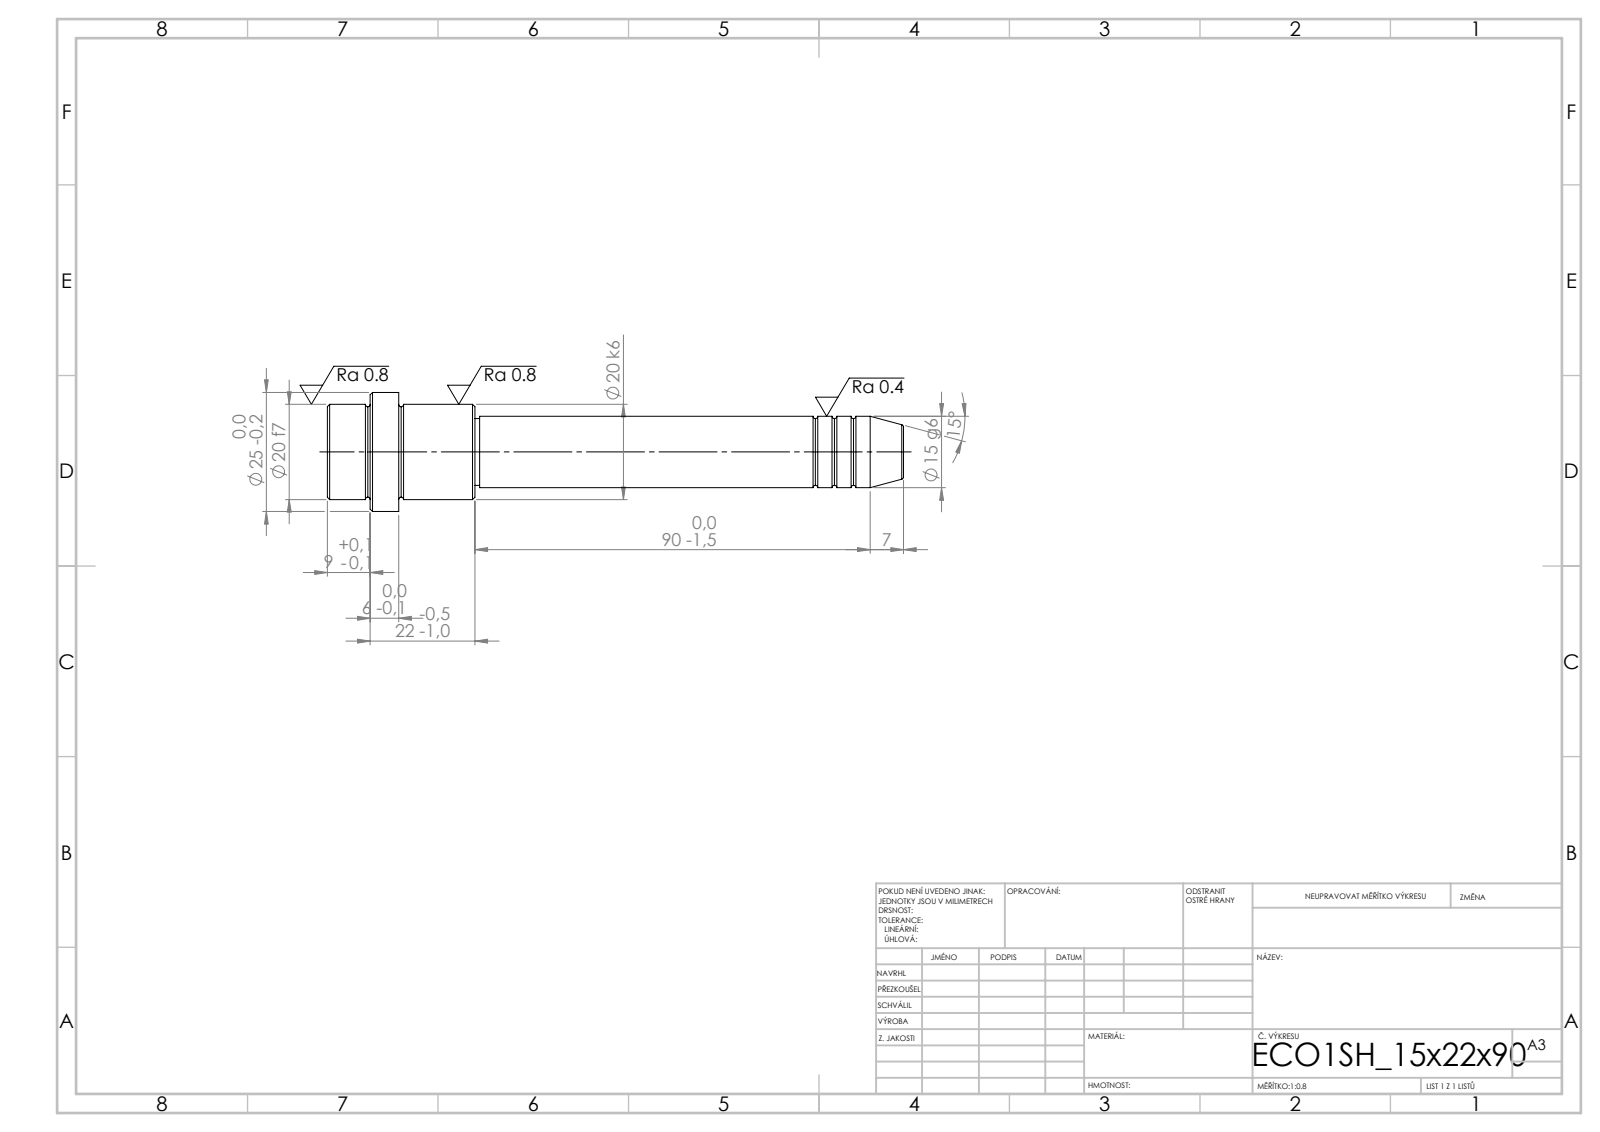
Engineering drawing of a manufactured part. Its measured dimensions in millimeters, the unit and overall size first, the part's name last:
Units: millimetres
Overall size (bounding box): 121 × 25 × 25
Round bosses / shafts (diameter × count): ⌀25 ×1, ⌀20 ×1, ⌀15 ×1, ⌀14 ×1
Main face-to-face distances: 15, 6, 9, 16, 22, 31, 90, 106, 112, 121
Volume: 26 269 mm³ · Surface area: 7 271 mm²
Bodies: 1 solid, 52 faces (6 planar, 16 cylindrical, 30 other)
STEP written by: SolidWorks 2019 (CONFIG_CONTROL_DESIGN)
